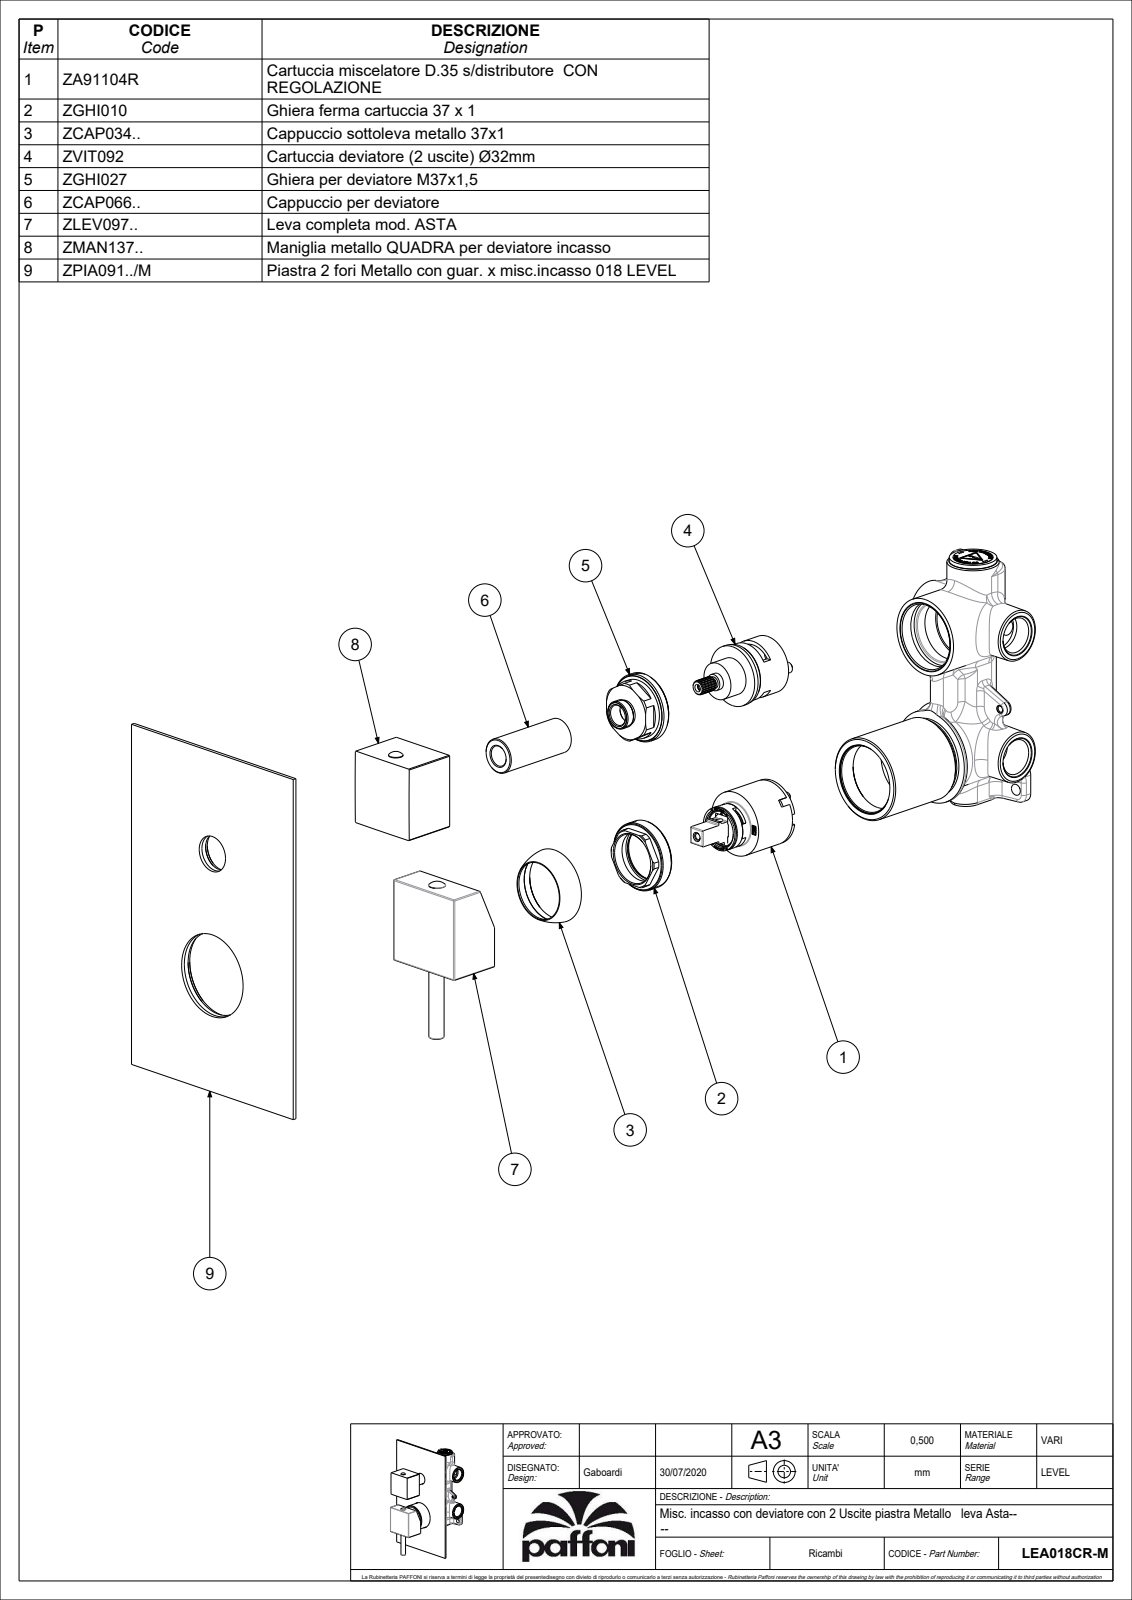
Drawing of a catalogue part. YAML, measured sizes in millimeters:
part_name: "LEA018CR-M"
step_written_by: "CREO PARAMETRIC BY PTC INC, 2020044 (CONFIG_CONTROL_DESIGN)"
units: millimeters
bodies: {solids: 4, faces: 1013, planar: 614, cylindrical: 242, other: 157}
overall_size: [190, 120, 56.39]
volume: 122276
surface_area: 99852
round_holes:
  - {diameter: 4, count: 2}
  - {diameter: 5.5, count: 2}
  - {diameter: 19.5, count: 2}
  - {diameter: 36, count: 2}
  - {diameter: 3, count: 1}
  - {diameter: 3.2, count: 1}
  - {diameter: 3.3, count: 1}
  - {diameter: 4.2, count: 1}
  - {diameter: 4.5, count: 1}
  - {diameter: 5, count: 1}
  - {diameter: 6, count: 1}
  - {diameter: 8.1, count: 1}
round_bosses_or_shafts:
  - {diameter: 5, count: 2}
  - {diameter: 44.8, count: 1}
  - {diameter: 35, count: 1}
  - {diameter: 25, count: 1}
  - {diameter: 23.5, count: 1}
  - {diameter: 23.4, count: 1}
  - {diameter: 21.8, count: 1}
  - {diameter: 18.7, count: 1}
partial_cylinders:
  - {radius: 0.5, count: 16}
  - {radius: 0.15, count: 11}
  - {radius: 0.3, count: 4}
  - {radius: 1, count: 2}
  - {radius: 7, count: 1}
  - {radius: 9.3, count: 1}
  - {radius: 10.85, count: 1}
  - {radius: 11.25, count: 1}
face_to_face_distances: [2, 40, 2.5, 42.5, 45, 55.1, 53.1, 3, 25.5, 110.5]
hole_center_spacings: [10, 14.6, 14.8, 58, 68]
